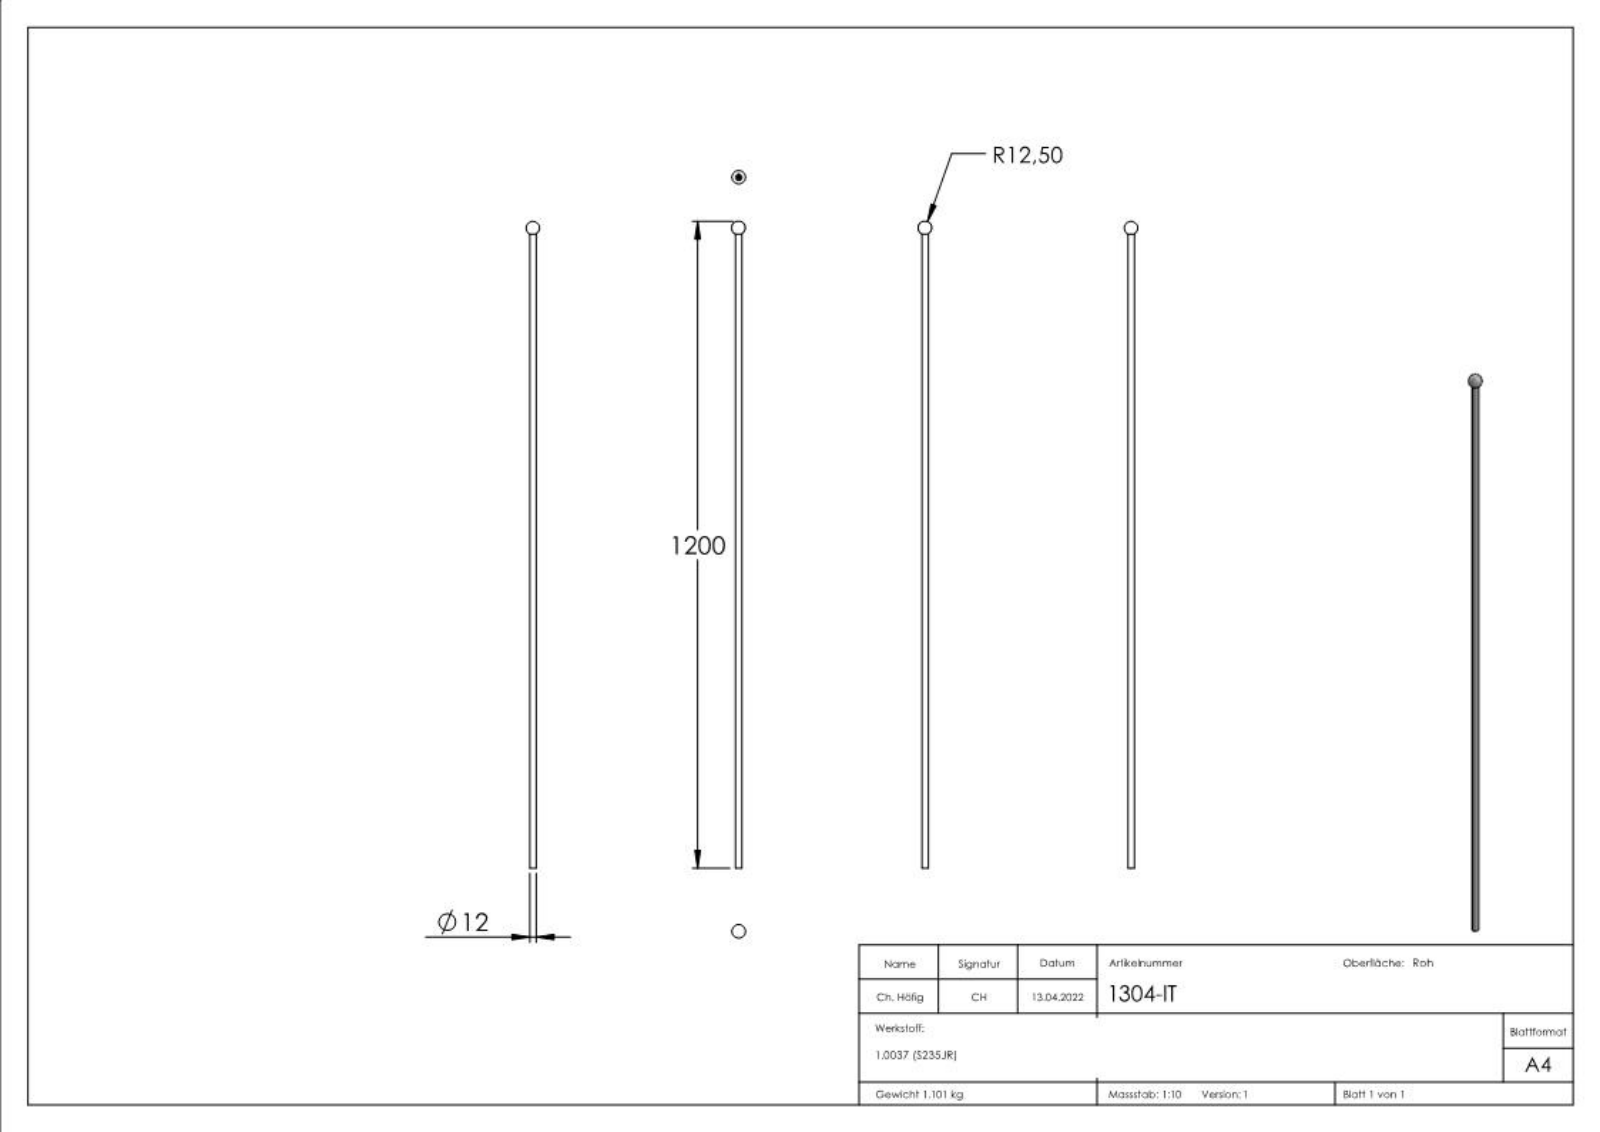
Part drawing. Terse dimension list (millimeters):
name: 1304-IT
written by: SolidWorks 2018 (CONFIG_CONTROL_DESIGN)
unit: mm
bodies: 1 solid, 229 faces (136 planar, 1 cylindrical, 92 other)
size: 1200 × 25 × 25
volume: 141 156 mm³; area: 46 317 mm²
bosses: 1× ⌀12
face distances: 1.76, 2.32, 1.96, 0.49, 0.47, 1.94, 2.45, 0.74, 0.54, 0.36
